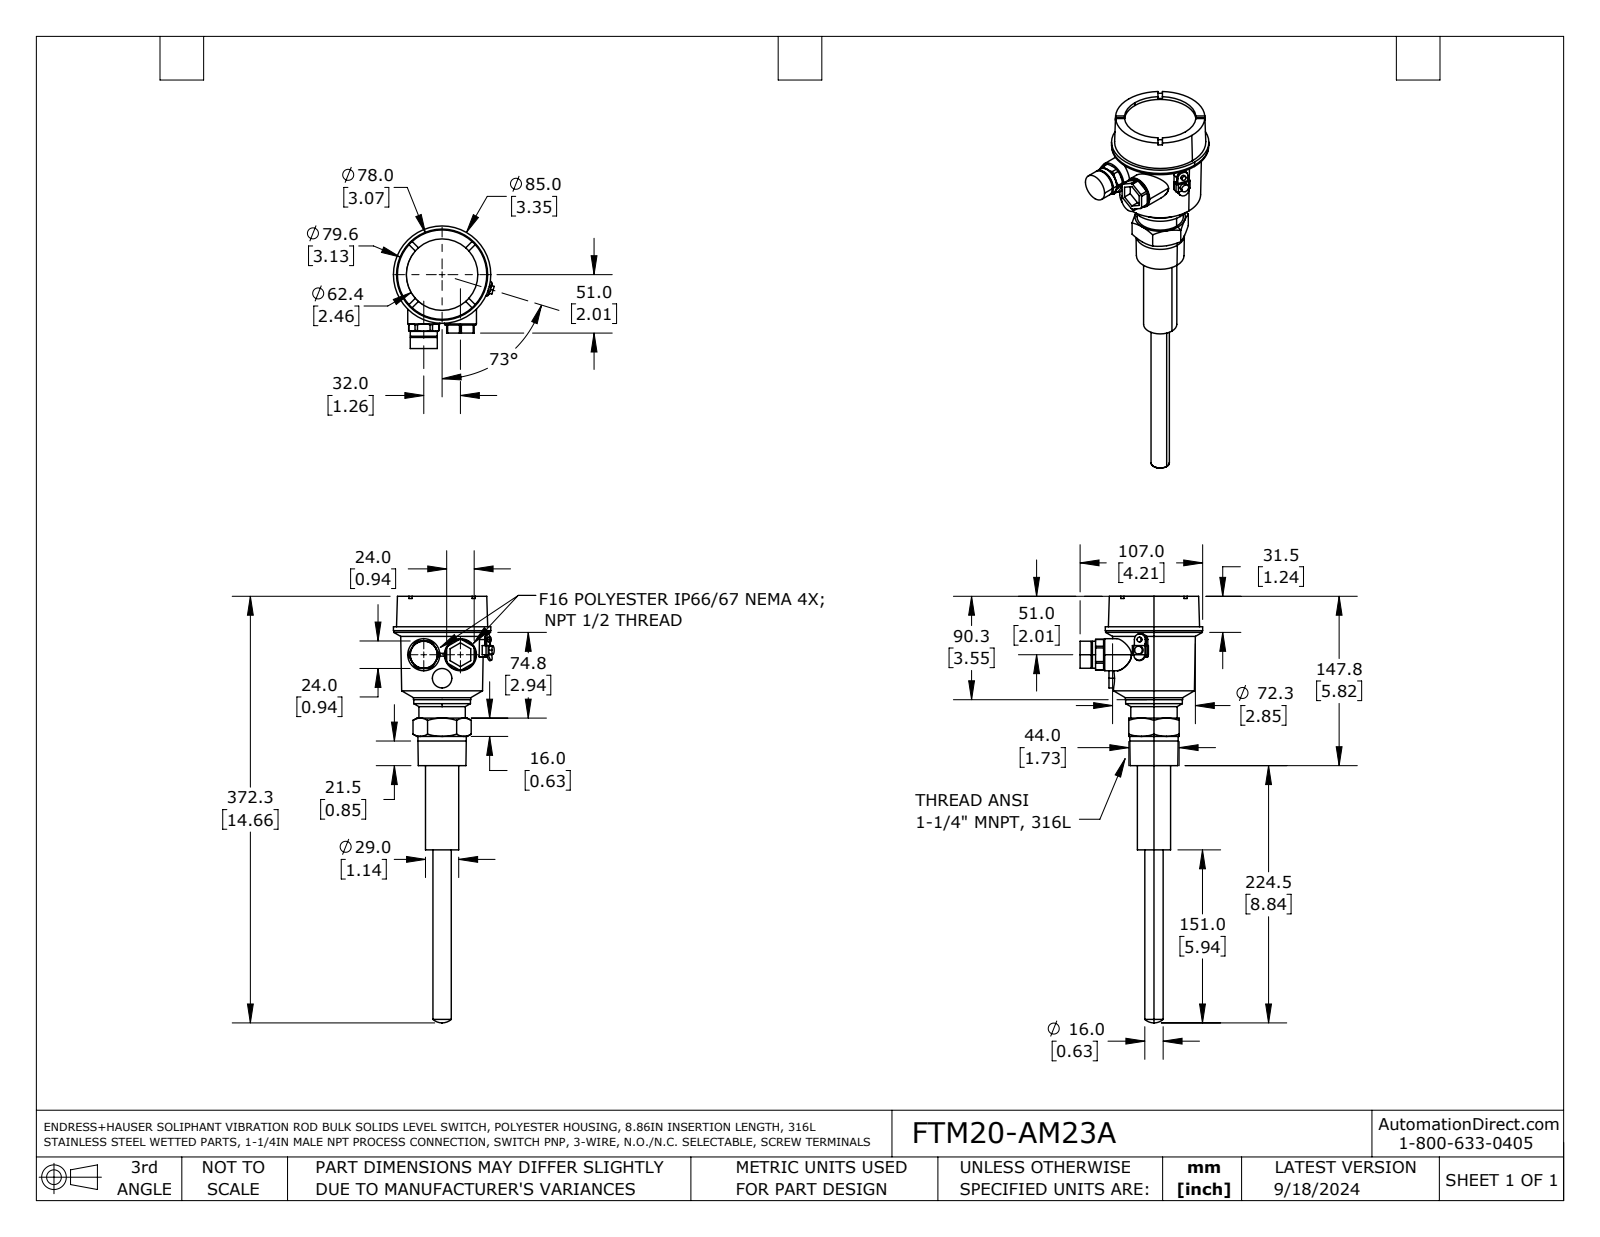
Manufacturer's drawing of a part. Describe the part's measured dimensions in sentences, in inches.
The part is named "FTM20-AM23A". Its 3-D file was written by "SolidWorks 2021 (AUTOMOTIVE_DESIGN)". It is 1 solid with 222 faces: 112 planar, 56 cylindrical and 54 other. Overall it measures 14.657 by 4.213 by 3.464 inches. Its volume is 34.74 cubic inches and its surface area 92.31 square inches. Round holes: 1 of diameter 2.457. Round bosses or shafts: 2 of diameter 1.102, 1 of diameter 3.346, 1 of diameter 3.327, 1 of diameter 1.969, 1 of diameter 1.949, 1 of diameter 1.661, 1 of diameter 1.594, 1 of diameter 1.142. Partial cylindrical surfaces (rounded edges, fillets, slot ends): 3 of radius 0.059, 1 of radius 0.197, 1 of radius 0.52. The main face-to-face distances are 0.118, 1.732, 0.929, 1.047, 4.772, 5.701, 5.819, 0.827, 2.894, 7.665.
